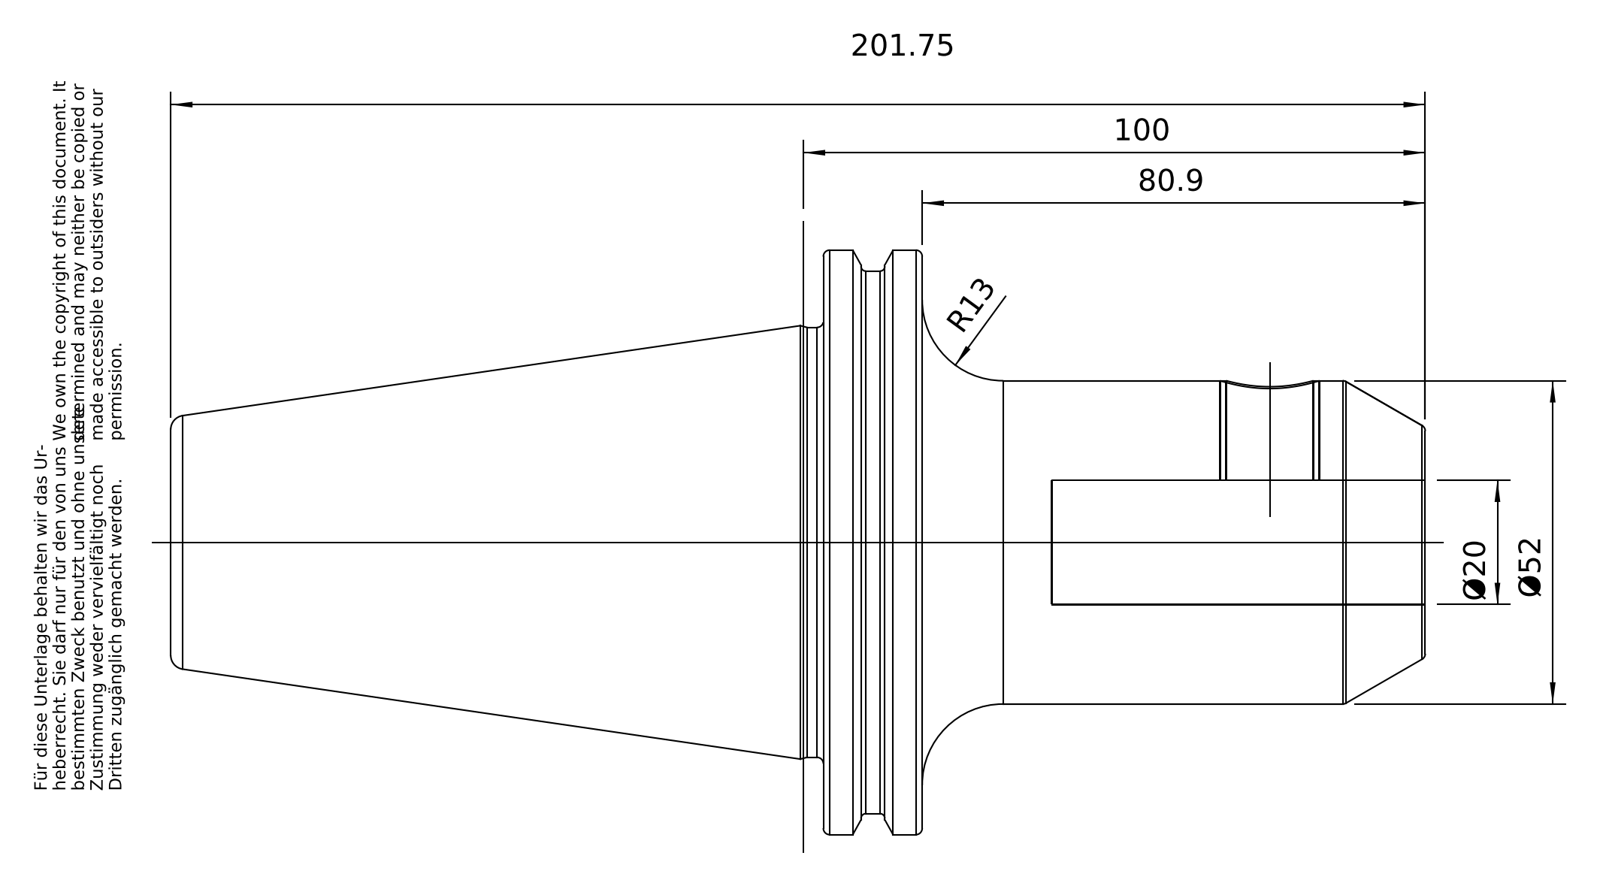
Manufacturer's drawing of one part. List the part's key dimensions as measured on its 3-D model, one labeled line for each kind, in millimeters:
Part name (STEP PRODUCT): 50-301-20
STEP written by: PRO/ENGINEER BY PARAMETRIC TECHNOLOGY CORPORATION, 2010430 (CONFIG_CONTROL_DESIGN)
Units: millimetres
Bodies: 1 solid, 104 faces (22 planar, 32 cylindrical, 50 other)
Overall size (bounding box): 201.6 × 97.47 × 94
Volume: 489 248 mm³ · Surface area: 58 973 mm²
Round holes (diameter × count): ⌀14 ×1, ⌀16 ×1, ⌀20 ×1, ⌀20.75 ×1, ⌀25.01 ×1, ⌀25.7 ×1
Round bosses / shafts (diameter × count): ⌀91 ×1, ⌀69.15 ×1, ⌀52 ×1, ⌀24.01 ×1
Partial cylindrical surfaces — rounded edges, fillets, slot ends (radius × count): R1.75 ×5, R48.74 ×1
Main face-to-face distances: 15.85, 96.8, 80.95, 104.8, 120.65, 201.6, 72.8, 141.5, 36.7, 20.85
